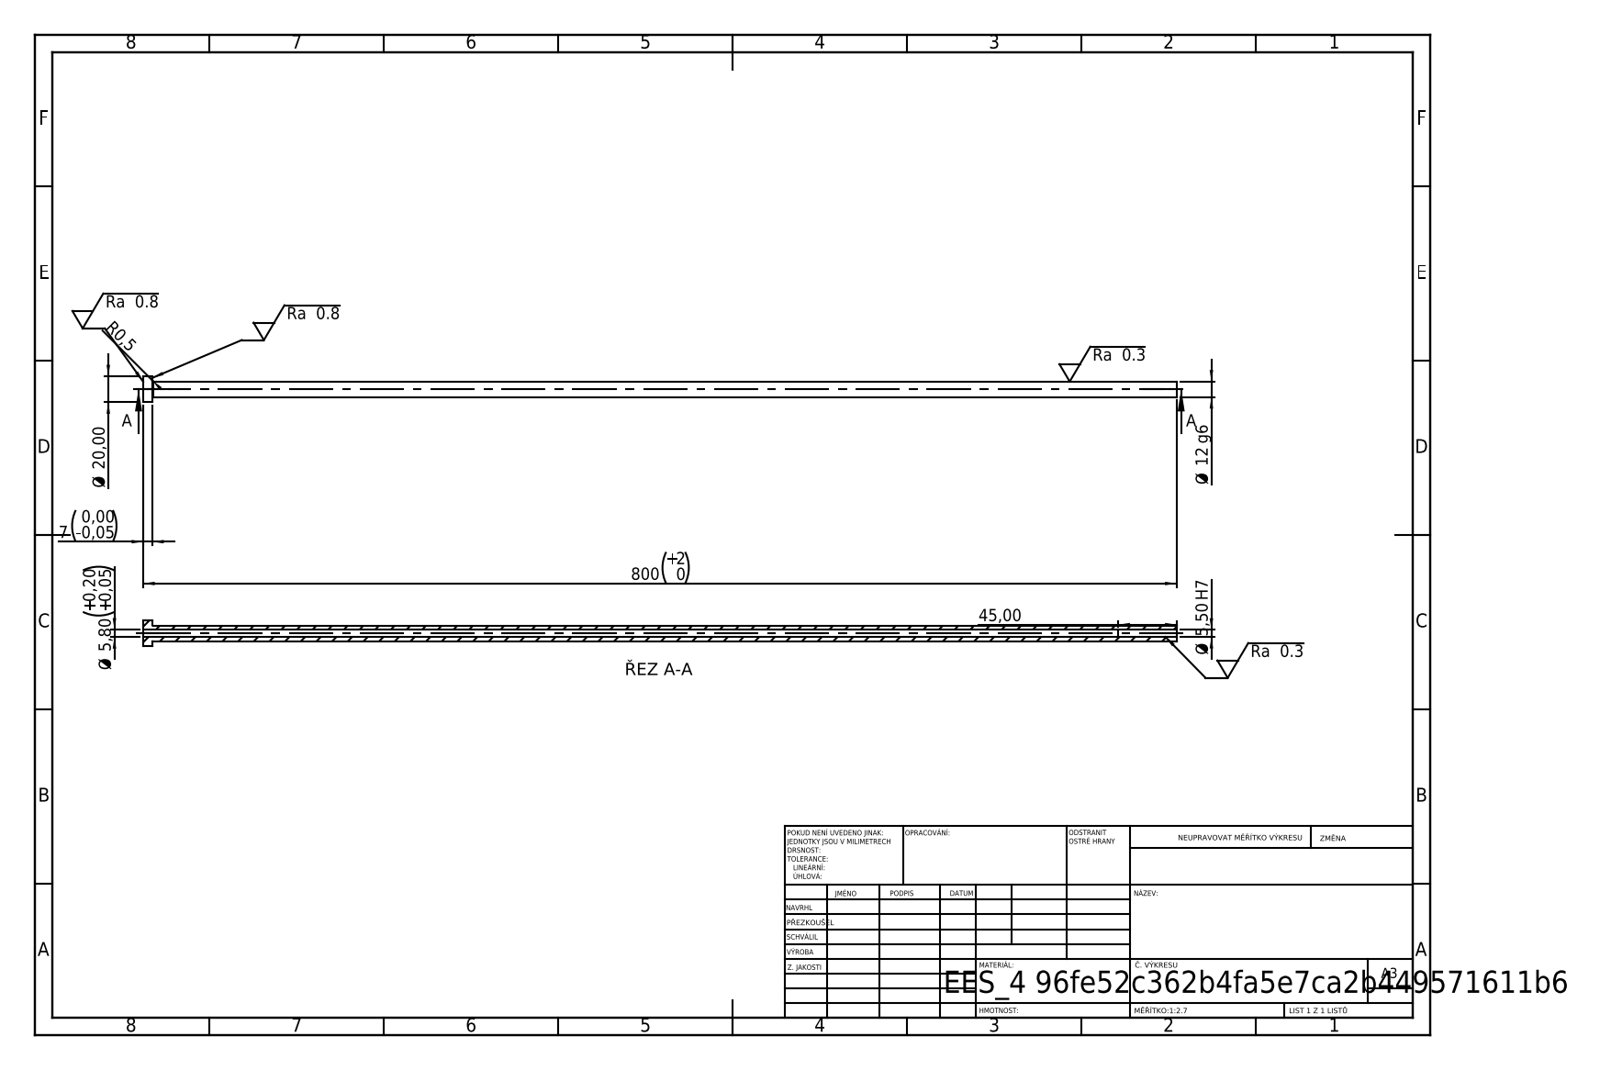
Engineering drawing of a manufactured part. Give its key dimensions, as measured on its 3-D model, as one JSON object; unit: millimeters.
{"step_written_by": "SolidWorks 2019 (CONFIG_CONTROL_DESIGN)", "units": "millimeters", "bodies": {"solids": 1, "faces": 14, "planar": 4, "cylindrical": 8, "other": 2}, "overall_size": [800, 20, 20], "volume_mm3": 70871, "surface_area_mm2": 45443, "round_holes": [[5.5, 1], [5.8, 1]], "round_bosses_or_shafts": [[20, 1], [12, 1]], "face_to_face_distances": [7, 800, 793, 755, 748, 45]}
